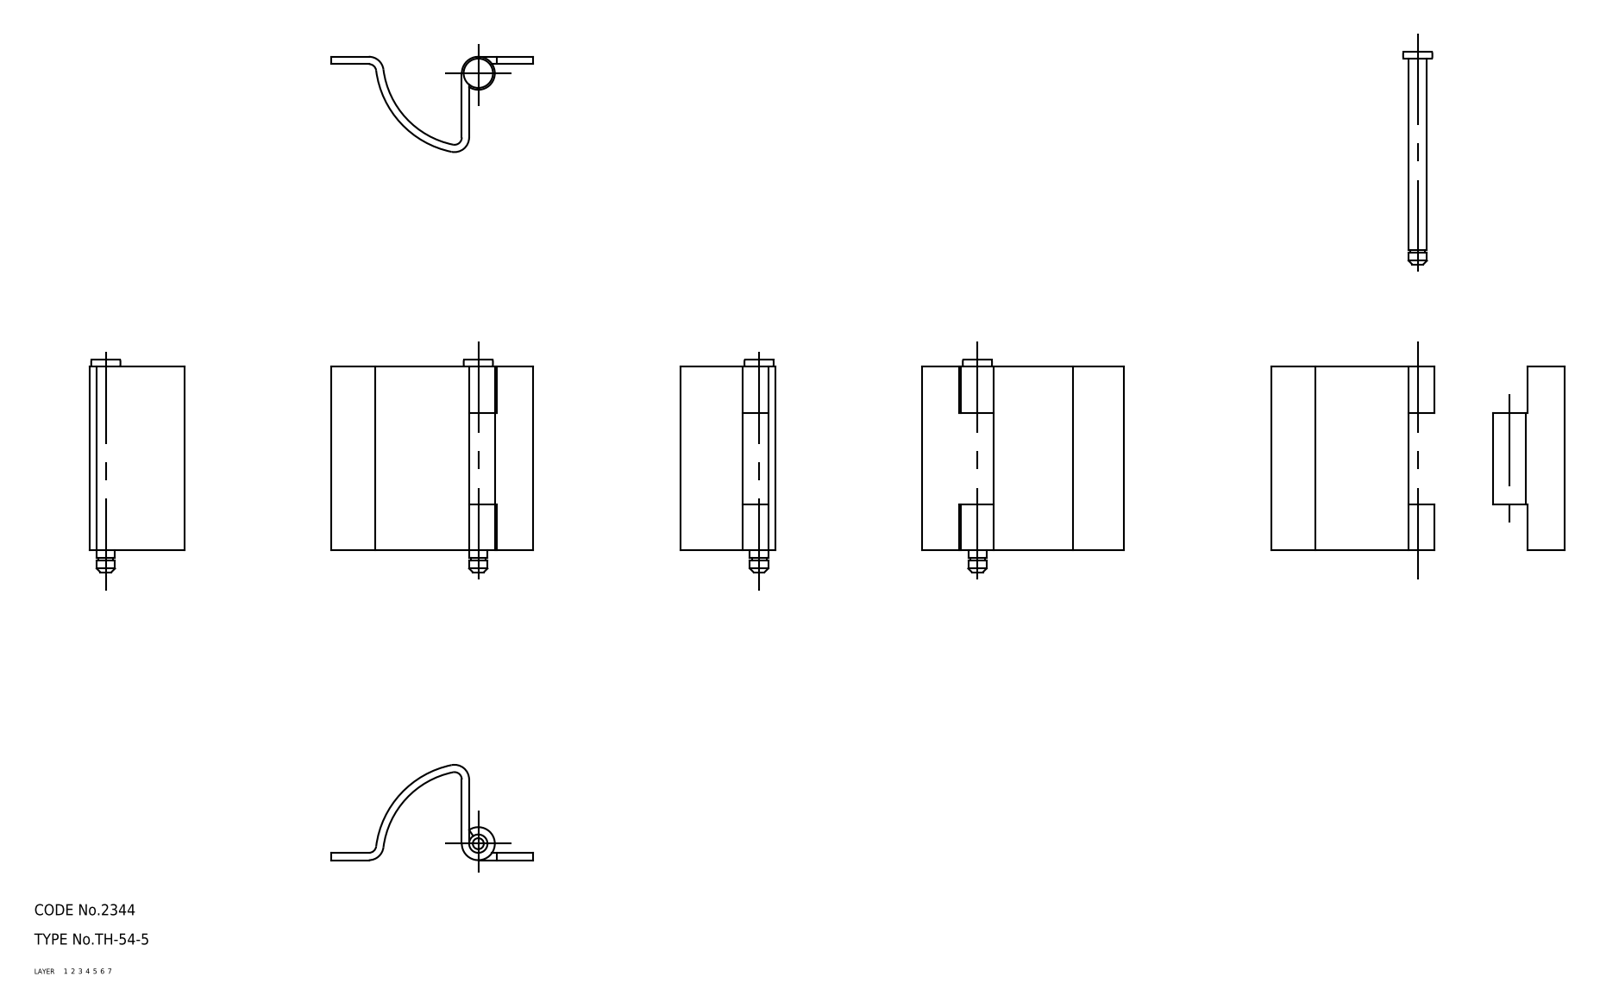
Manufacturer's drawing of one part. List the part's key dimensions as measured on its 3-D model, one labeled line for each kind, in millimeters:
Part name (STEP PRODUCT): shaft; hinge piece_B; hinge piece_A; TH_54_5_11250_36
STEP written by: CADfix (AUTOMOTIVE_DESIGN)
Units: millimetres
Bodies: 3 solids, 48 faces (0 planar, 0 cylindrical, 48 other)
Overall size (bounding box): 58 × 55 × 26
Volume: 10 898 mm³ · Surface area: 11 709 mm²
